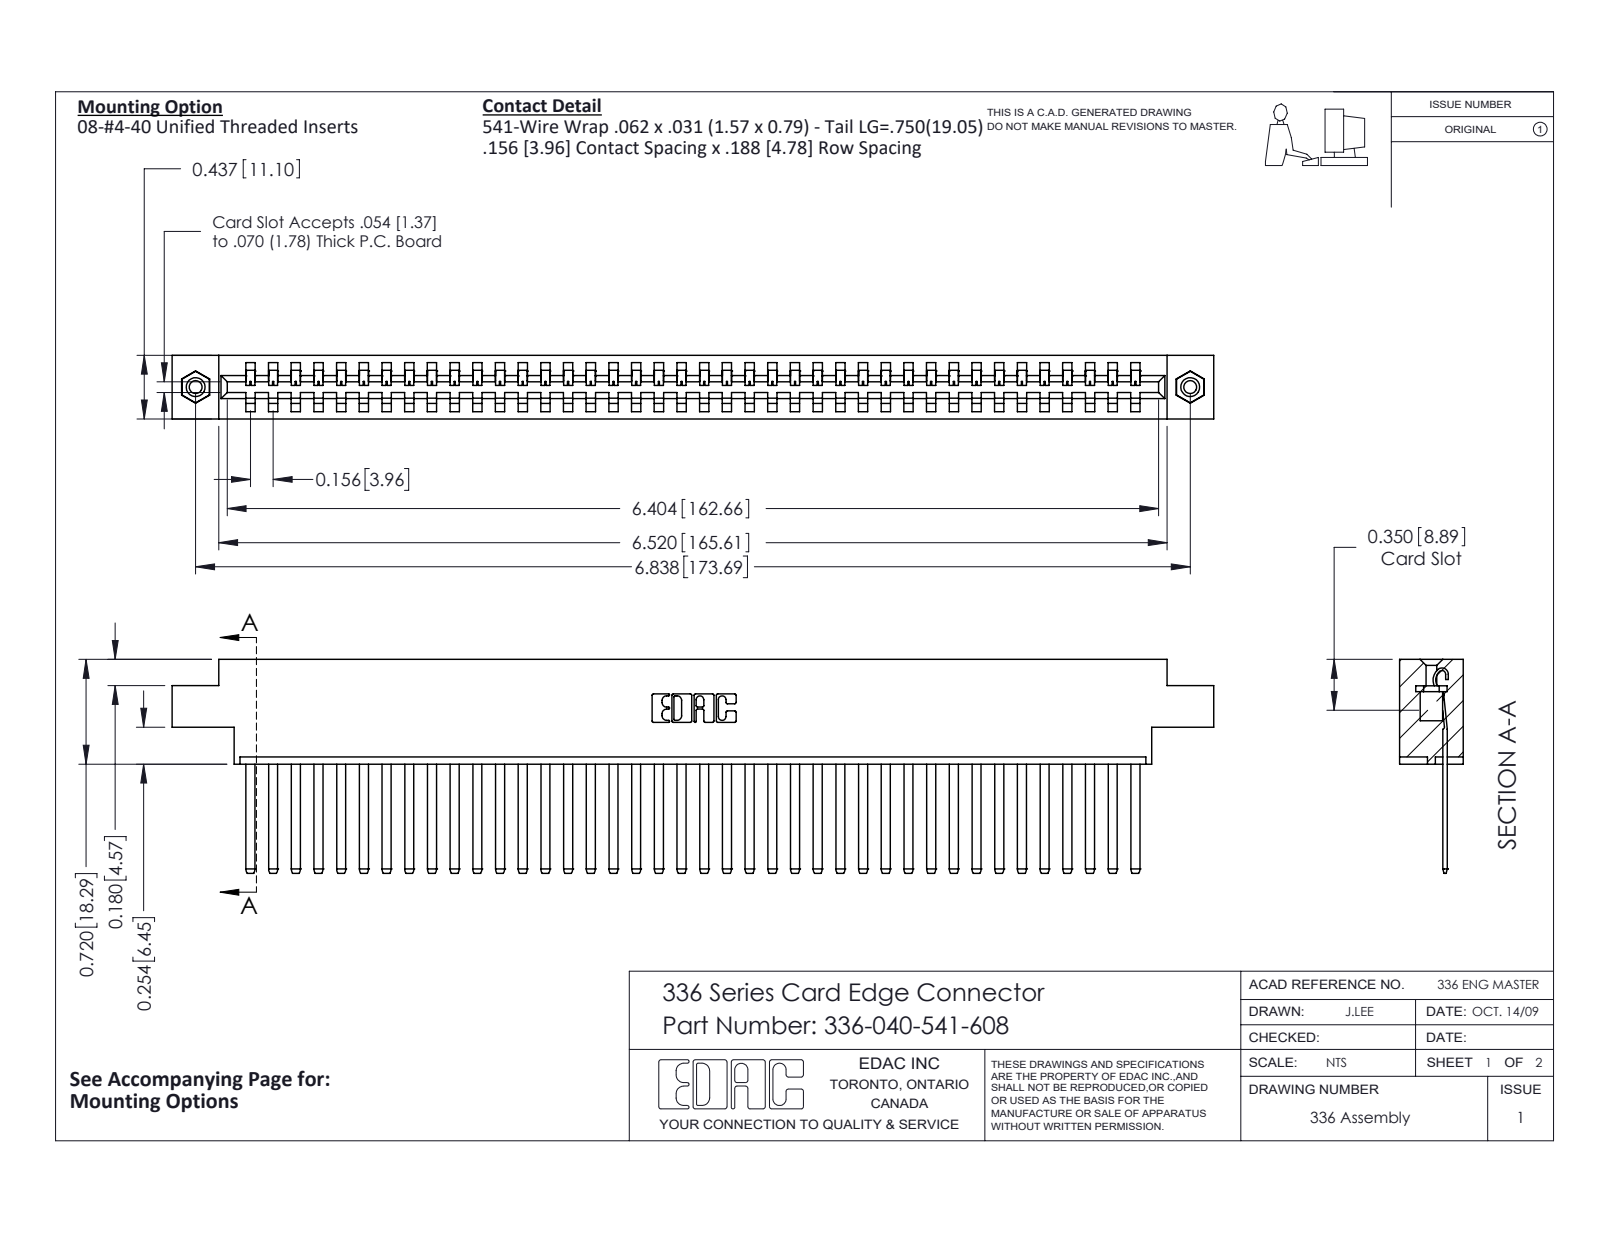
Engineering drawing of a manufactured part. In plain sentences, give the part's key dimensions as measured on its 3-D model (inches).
The part is named "336 Part_Offset - .156 Dia - TI; 345-250-001_345-250-003-102; 336-290-001_336-290-541; 336-040-541-608". Its 3-D file was written by "SolidWorks 2020 (CONFIG_CONTROL_DESIGN)". It is 43 solids with 2178 faces: 1466 planar, 696 cylindrical and 16 other. Overall it measures 7.161 by 1.47 by 0.437 inches. Its volume is 1.613 cubic inches and its surface area 44.73 square inches. Round holes: 2 of diameter 0.089, 2 of diameter 0.125, 2 of diameter 0.156. Round bosses or shafts: 2 of diameter 0.155. Partial cylindrical surfaces (rounded edges, fillets, slot ends): 80 of radius 0.004, 80 of radius 0.056, 22 of radius 0.01, 6 of radius 0.007, 6 of radius 0.031, 3 of radius 0.026, 2 of radius 0.022, 2 of radius 0.04. The main face-to-face distances are 0.437, 0.181, 0.328, 0.14, 0.297, 0.109, 0.031, 0.256, 0.05, 0.131. The hole center spacings are 6.838.
